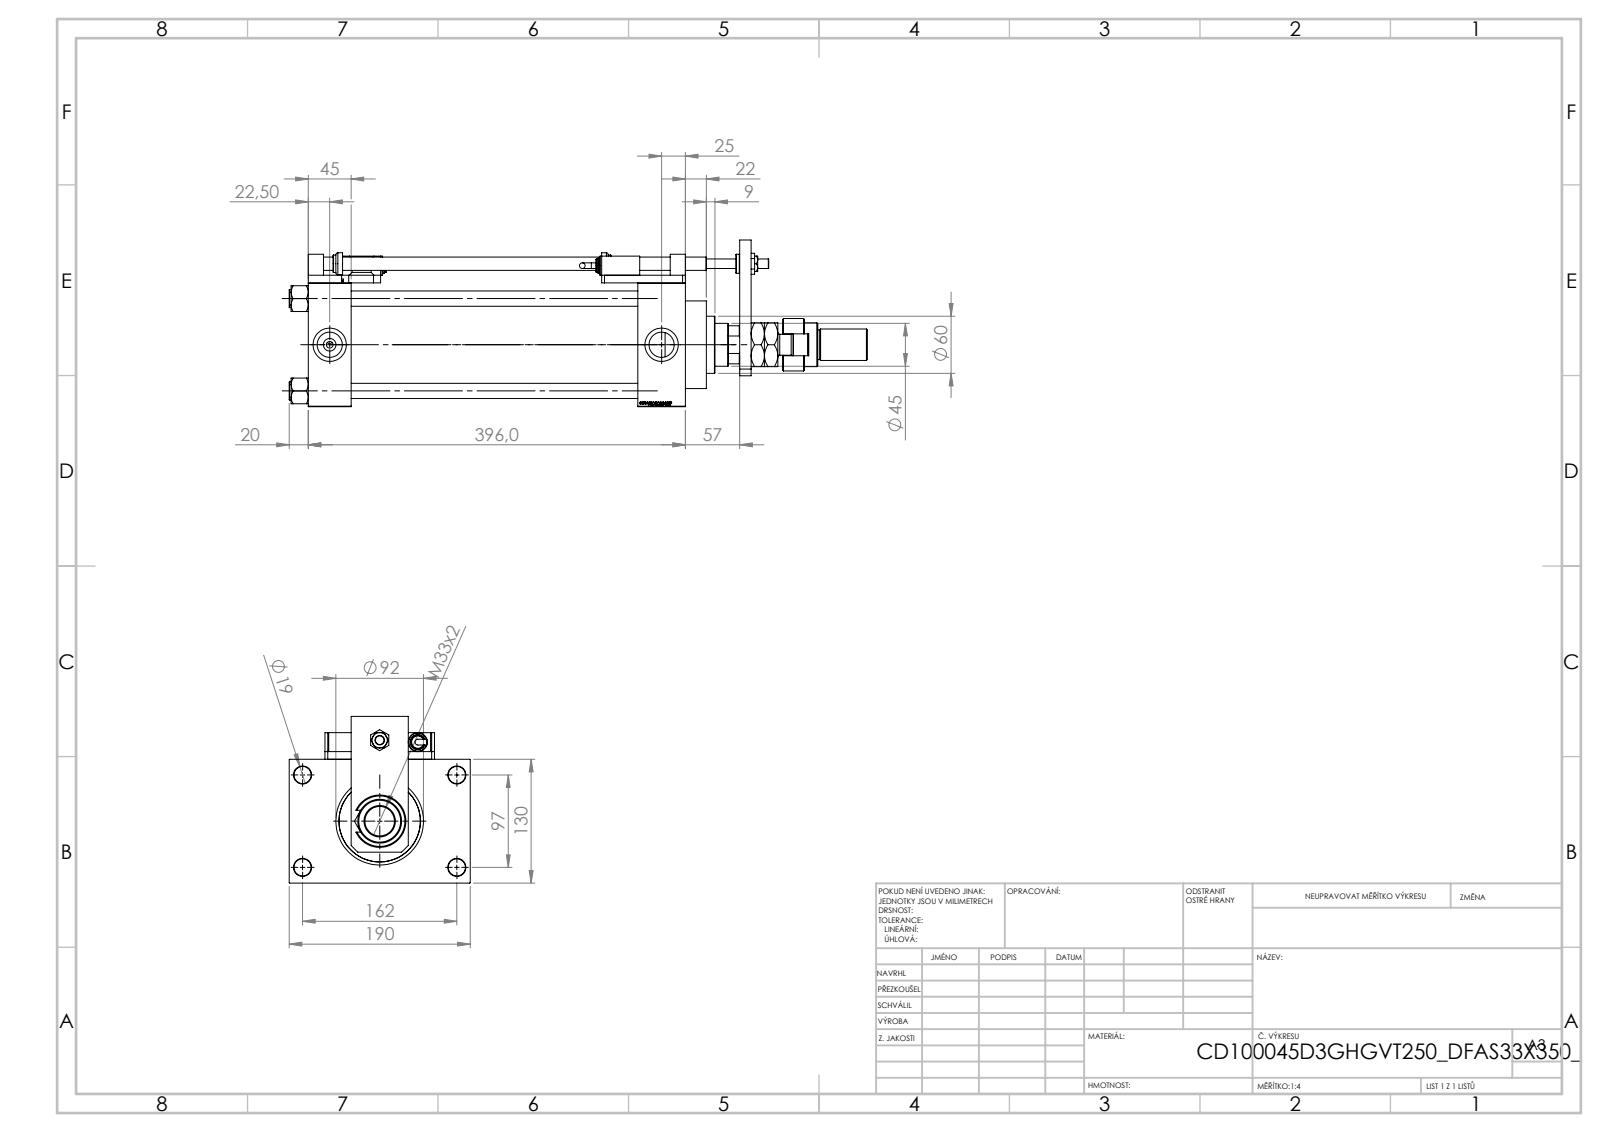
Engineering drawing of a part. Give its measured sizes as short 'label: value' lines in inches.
name: V215CD_SWITCH_Q_MAGNET; V215CD_D_Body; MFA; V215CD_C_DFAS_SWITCH (+7 more)
written by: SolidWorks 2019 (CONFIG_CONTROL_DESIGN)
unit: in
bodies: 28 solids, 1565 faces (742 planar, 180 cylindrical, 643 other)
size: 23.898 × 7.48 × 6.89
volume: 236.6 in³; area: 1 128 in²
holes: 4× ⌀0.335, 4× ⌀0.531, 4× ⌀0.63, 4× ⌀0.709, 4× ⌀1.041, 4× ⌀1.378, 3× ⌀0.276, 1× ⌀0.394, 1× ⌀0.551, 1× ⌀1.24, 1× ⌀1.299, 1× ⌀1.535
bosses: 4× ⌀0.748, 3× ⌀0.787, 2× ⌀0.63, 2× ⌀0.551, 2× ⌀0.236, 1× ⌀4.173, 1× ⌀3.622, 1× ⌀2.362
rounds: 4× R0.295, 1× R0.453, 1× R0.866
face distances: 1.772, 5.118, 15.591, 13.819, 0.315, 1.969, 13.622, 11.85, 5.433, 4.685
hole spacings: 1.281, 2.698, 3.717, 3.815, 4.026, 5.096, 6.367, 0.85
